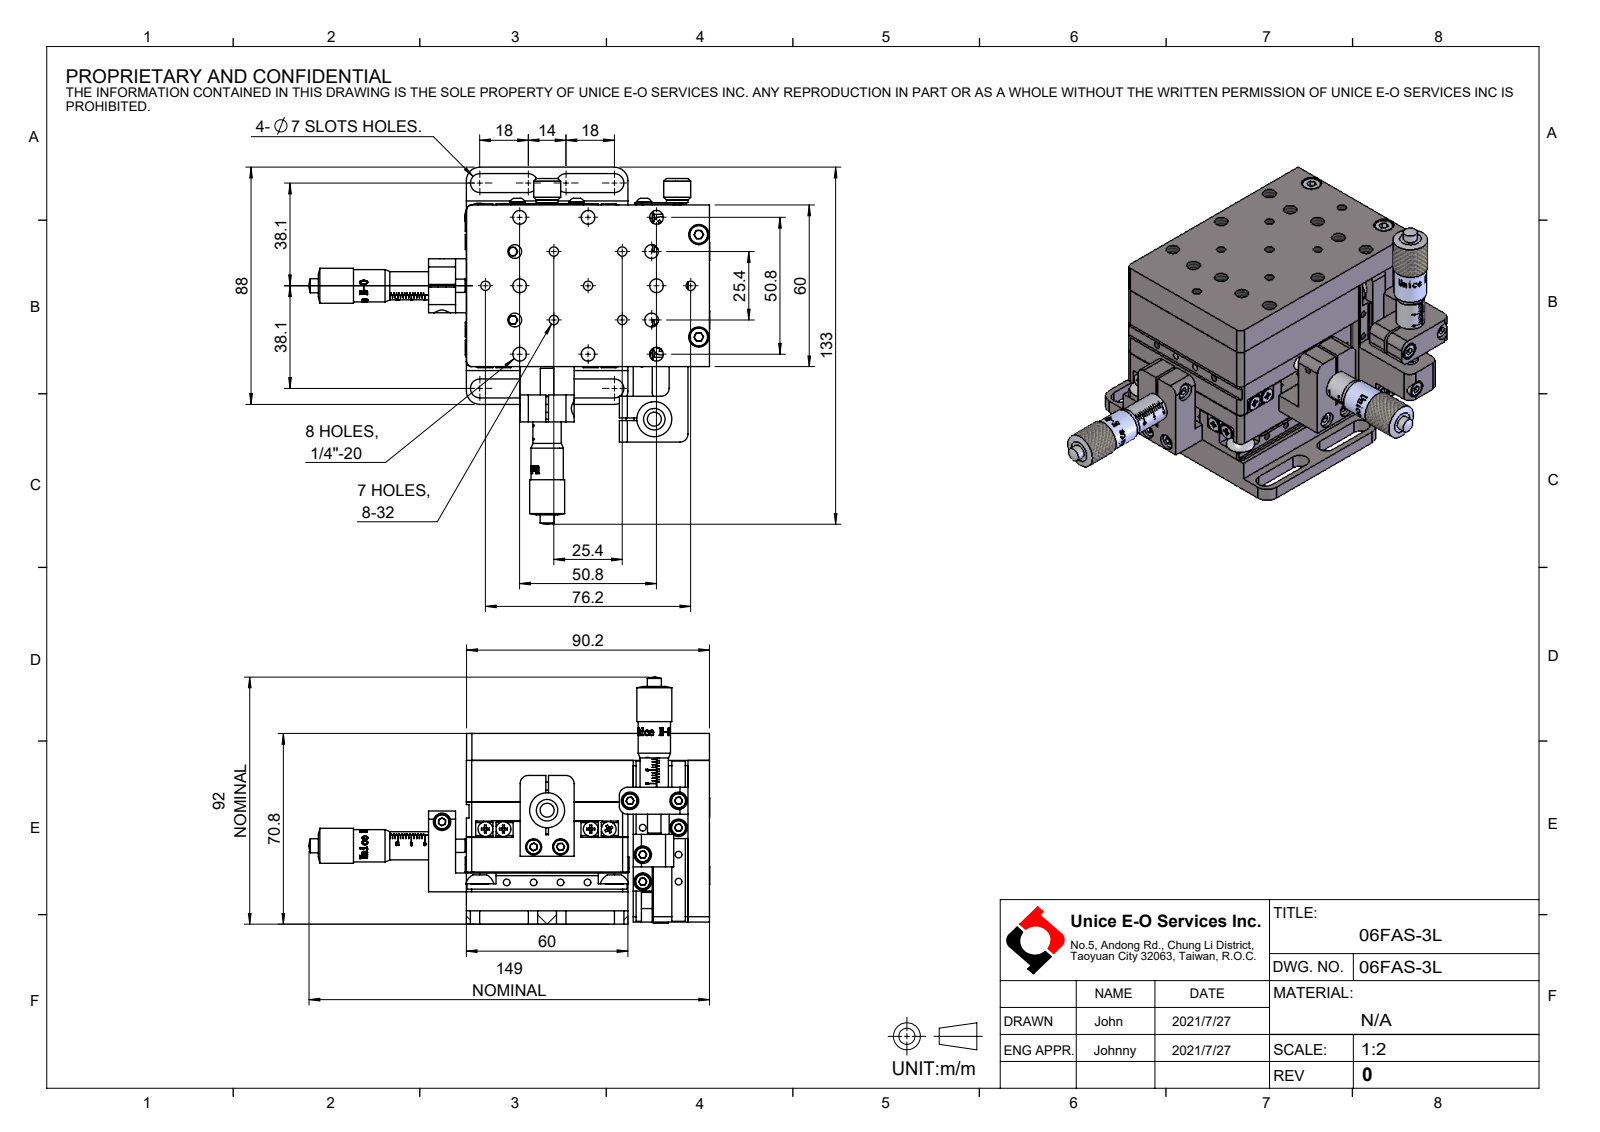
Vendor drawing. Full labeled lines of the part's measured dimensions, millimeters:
Part name (STEP PRODUCT): 06FAS-3L
STEP written by: SolidWorks 2020 (CONFIG_CONTROL_DESIGN)
Units: millimetres
Bodies: 0 solids, 1399 faces (818 planar, 372 cylindrical, 209 other)
Overall size (bounding box): 148.74 × 132.5 × 91.7
Round holes (diameter × count): ⌀2.5 ×18, ⌀5.11 ×18, ⌀6.5 ×9, ⌀2.05 ×8, ⌀3.45 ×7, ⌀6 ×6, ⌀7.54 ×4, ⌀3.1 ×2, ⌀7.5 ×2, ⌀9.5 ×1
Round bosses / shafts (diameter × count): ⌀5.5 ×18, ⌀7 ×6, ⌀5.7 ×4, ⌀13 ×3, ⌀12 ×3, ⌀10.5 ×3, ⌀9.2 ×3, ⌀5.2 ×3
Partial cylindrical surfaces — rounded edges, fillets, slot ends (radius × count): R3 ×11, R2 ×10, R3.5 ×8, R1.75 ×4, R5 ×4, R5.98 ×3
Main face-to-face distances: 7, 15.4, 20.3, 13.1, 13.3, 60, 13.2, 10, 25.4, 60.8
Hole centre spacings: 25.4, 40.16, 17.96, 10, 35.92, 28.4, 56.8, 50.8
